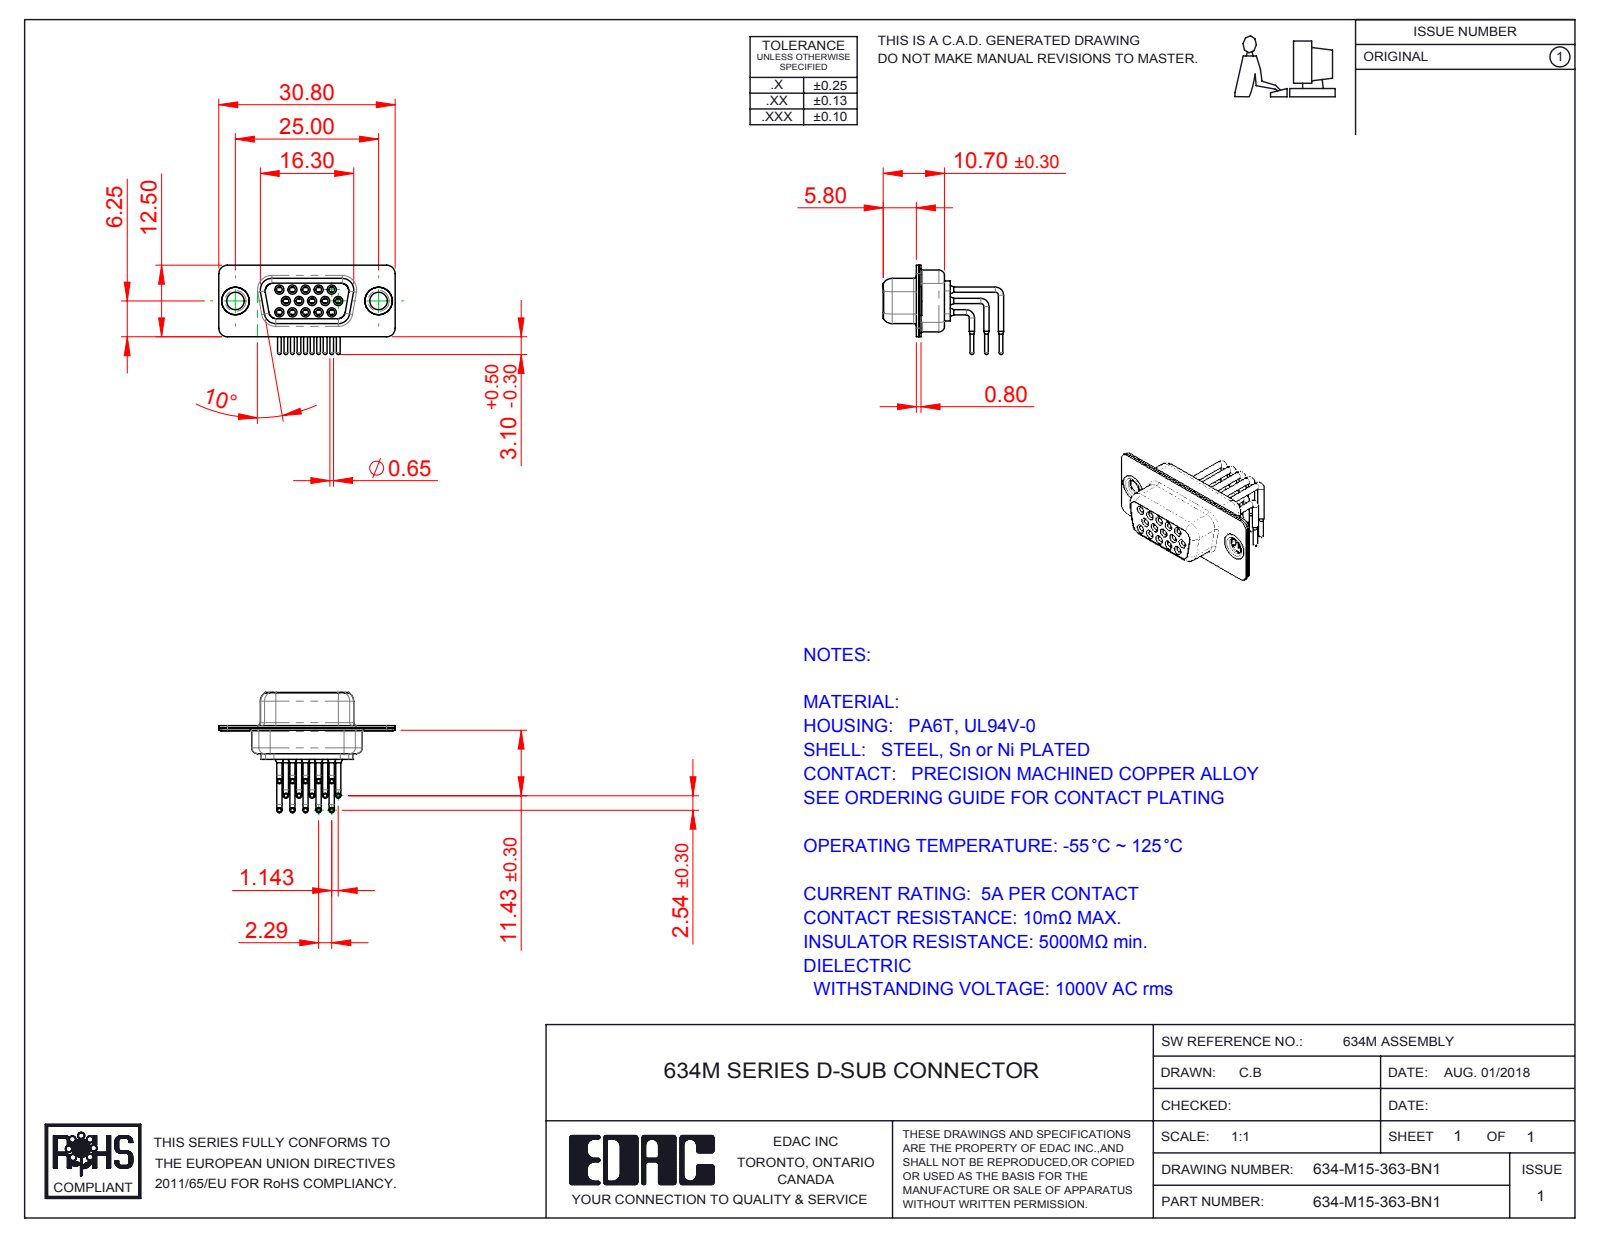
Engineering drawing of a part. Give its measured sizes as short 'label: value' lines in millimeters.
name: 634M Contact Row 2; 634M Contact Row 3; 634M Contact Row 1; 634M Thru Hole Rivet (+4 more)
written by: SolidWorks 2016 (CONFIG_CONTROL_DESIGN)
unit: mm
bodies: 20 solids, 1048 faces (292 planar, 466 cylindrical, 290 other)
size: 30.8 × 21.02 × 15.6
volume: 1 661 mm³; area: 5 524 mm²
holes: 15× ⌀1, 15× ⌀1.1, 15× ⌀1.7, 15× ⌀1.8, 15× ⌀2, 2× ⌀3.05, 2× ⌀4, 2× ⌀4.8
bosses: 30× ⌀0.9, 15× ⌀1.6, 15× ⌀1.5, 15× ⌀0.65, 2× ⌀5, 2× ⌀4.9, 2× ⌀3.55, 1× ⌀2
rounds: 16× R1.5, 12× R2, 8× R1.35, 8× R1.6, 4× R0.25, 4× R0.5, 4× R0.6, 4× R0.65
face distances: 0.4, 0.8, 1.45, 2.3, 8.95, 1.9, 8.5, 0.85, 6.2, 9.35
hole spacings: 2.28, 3.96, 2.29, 4.57, 6.05, 6.04, 6.86, 7.92
